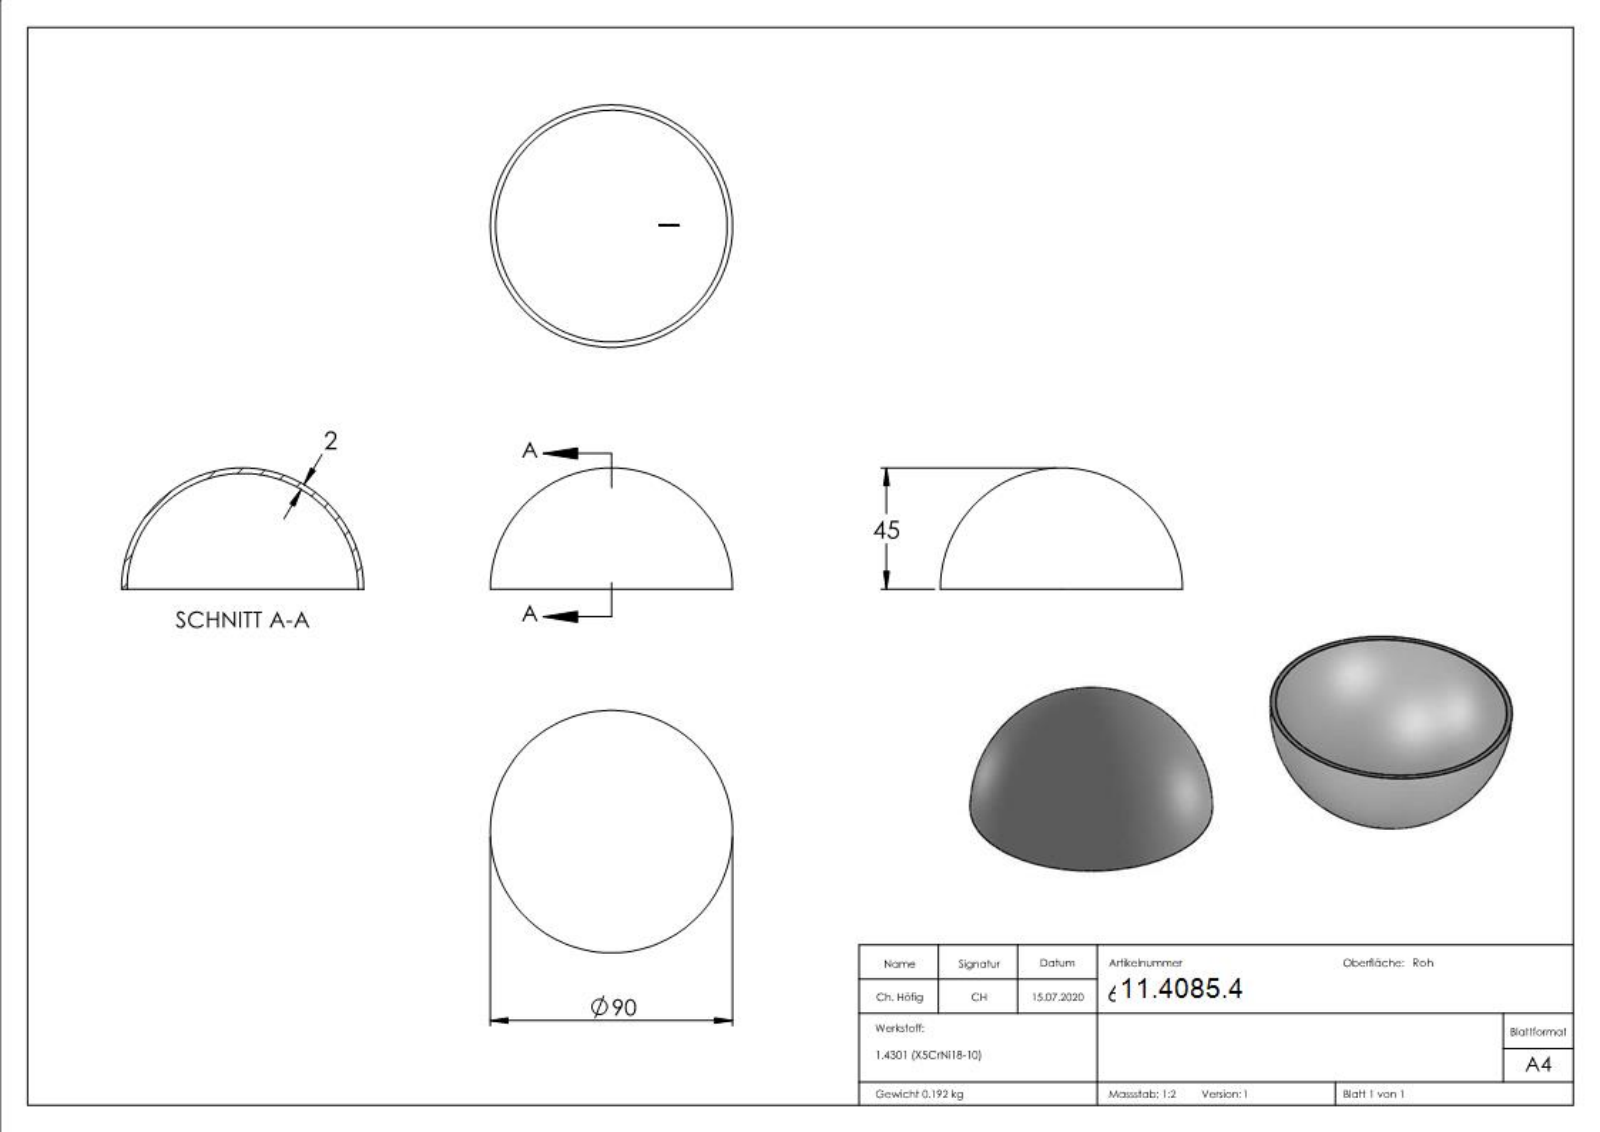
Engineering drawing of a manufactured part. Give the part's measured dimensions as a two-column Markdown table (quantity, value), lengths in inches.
| quantity | value |
| --- | --- |
| part name | 620090-VA |
| STEP written by | SolidWorks 2018 (CONFIG_CONTROL_DESIGN) |
| units | inches |
| bodies | 1 solid, 216 faces (89 planar, 0 cylindrical, 127 other) |
| overall size | 3.543 × 3.543 × 1.772 |
| volume | 1.485 in³ |
| surface area | 38.59 in² |
| main face-to-face distances | 0.018, 0.02, 0.024, 0.047, 0.021, 0.022, 0.032, 0.052, 0.033, 0.012 |
